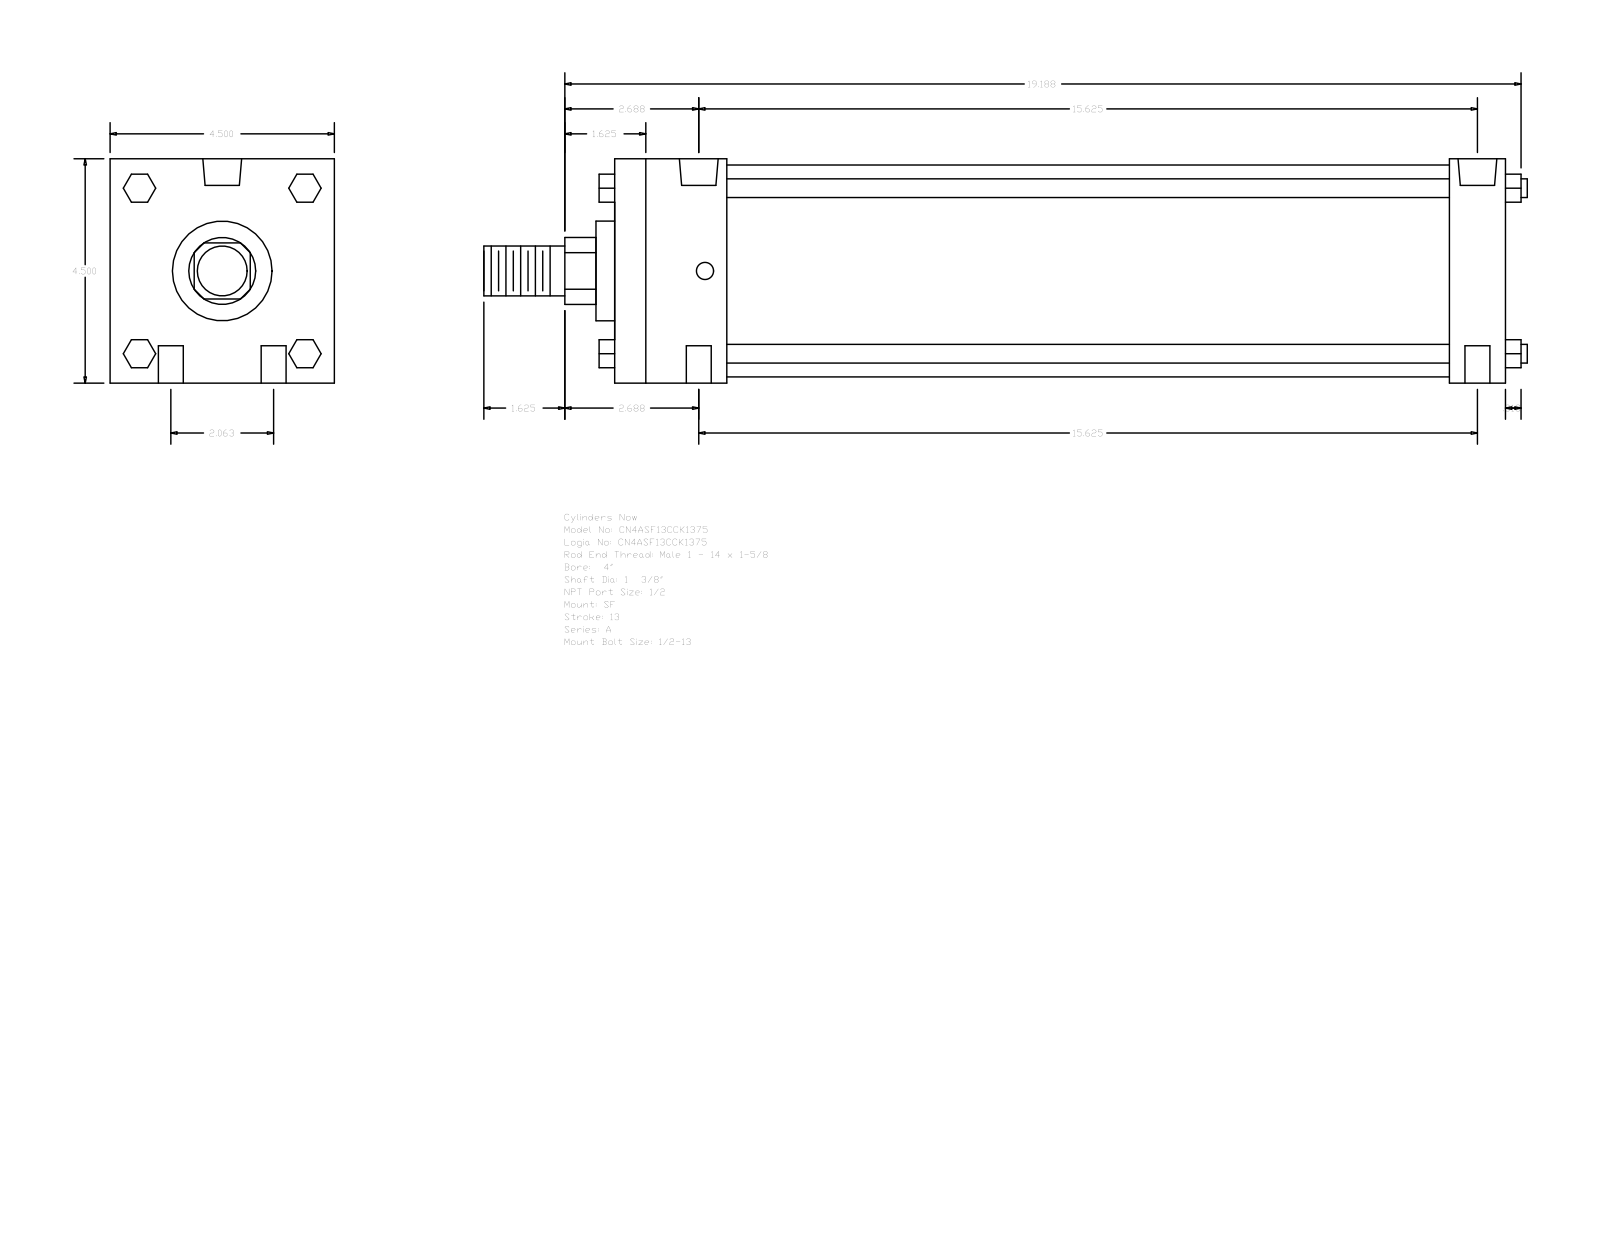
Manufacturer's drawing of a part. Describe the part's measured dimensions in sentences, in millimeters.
The part is named "A_SF__0400_1.375". Its 3-D file was written by "GSSL Pune (CONFIG_CONTROL_DESIGN)". It is 0 solids with 124 faces: 94 planar, 30 cylindrical and 0 other. Overall it measures 531.81 by 114.3 by 114.3 millimeters. Round holes: 4 of diameter 12.7, 2 of diameter 8.73, 2 of diameter 19.77. Round bosses or shafts: 4 of diameter 9.53, 1 of diameter 107.95, 1 of diameter 50.8, 1 of diameter 34.92, 1 of diameter 25.4. Partial cylindrical surfaces (rounded edges, fillets, slot ends): 1 of radius 17.06. The main face-to-face distances are 114.3, 454.03, 57.15, 28.58, 425.45, 368.3, 396.88, 66.67, 14.29, 9.52. The hole center spacings are 26.19, 397.74, 396.88, 52.38, 400.32, 390.52.
